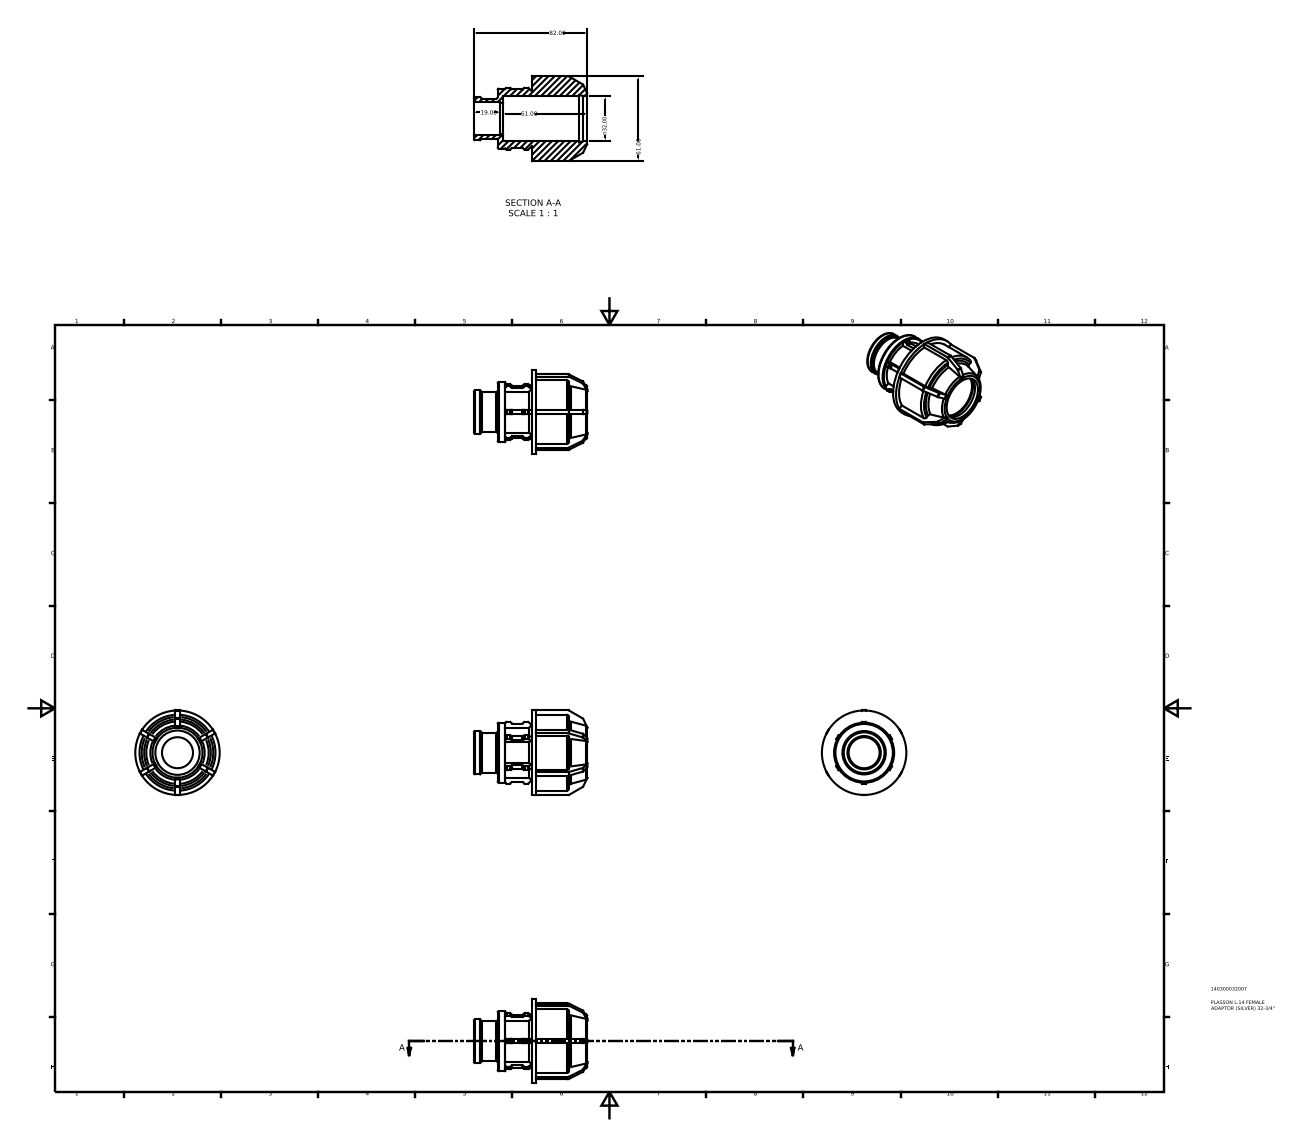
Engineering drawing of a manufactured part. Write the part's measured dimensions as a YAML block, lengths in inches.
part_name: "140300032007"
step_written_by: "Autodesk Inventor 2015 (AUTOMOTIVE_DESIGN)"
units: inches
bodies: {solids: 1, faces: 261, planar: 160, cylindrical: 68, other: 33}
overall_size: [3.228, 2.402, 2.402]
volume: 4.213
surface_area: 41.08
round_holes:
  - {diameter: 0.882, count: 1}
  - {diameter: 0.95, count: 1}
  - {diameter: 1.26, count: 1}
round_bosses_or_shafts:
  - {diameter: 2.402, count: 1}
  - {diameter: 2.161, count: 1}
  - {diameter: 1.709, count: 1}
  - {diameter: 1.424, count: 1}
  - {diameter: 1.234, count: 1}
  - {diameter: 1.139, count: 1}
partial_cylinders:
  - {radius: 0.038, count: 48}
face_to_face_distances: [0.12, 0.12, 0.968, 1.088, 0.152, 2.402, 0.12, 0.817, 0.937, 0.073]
